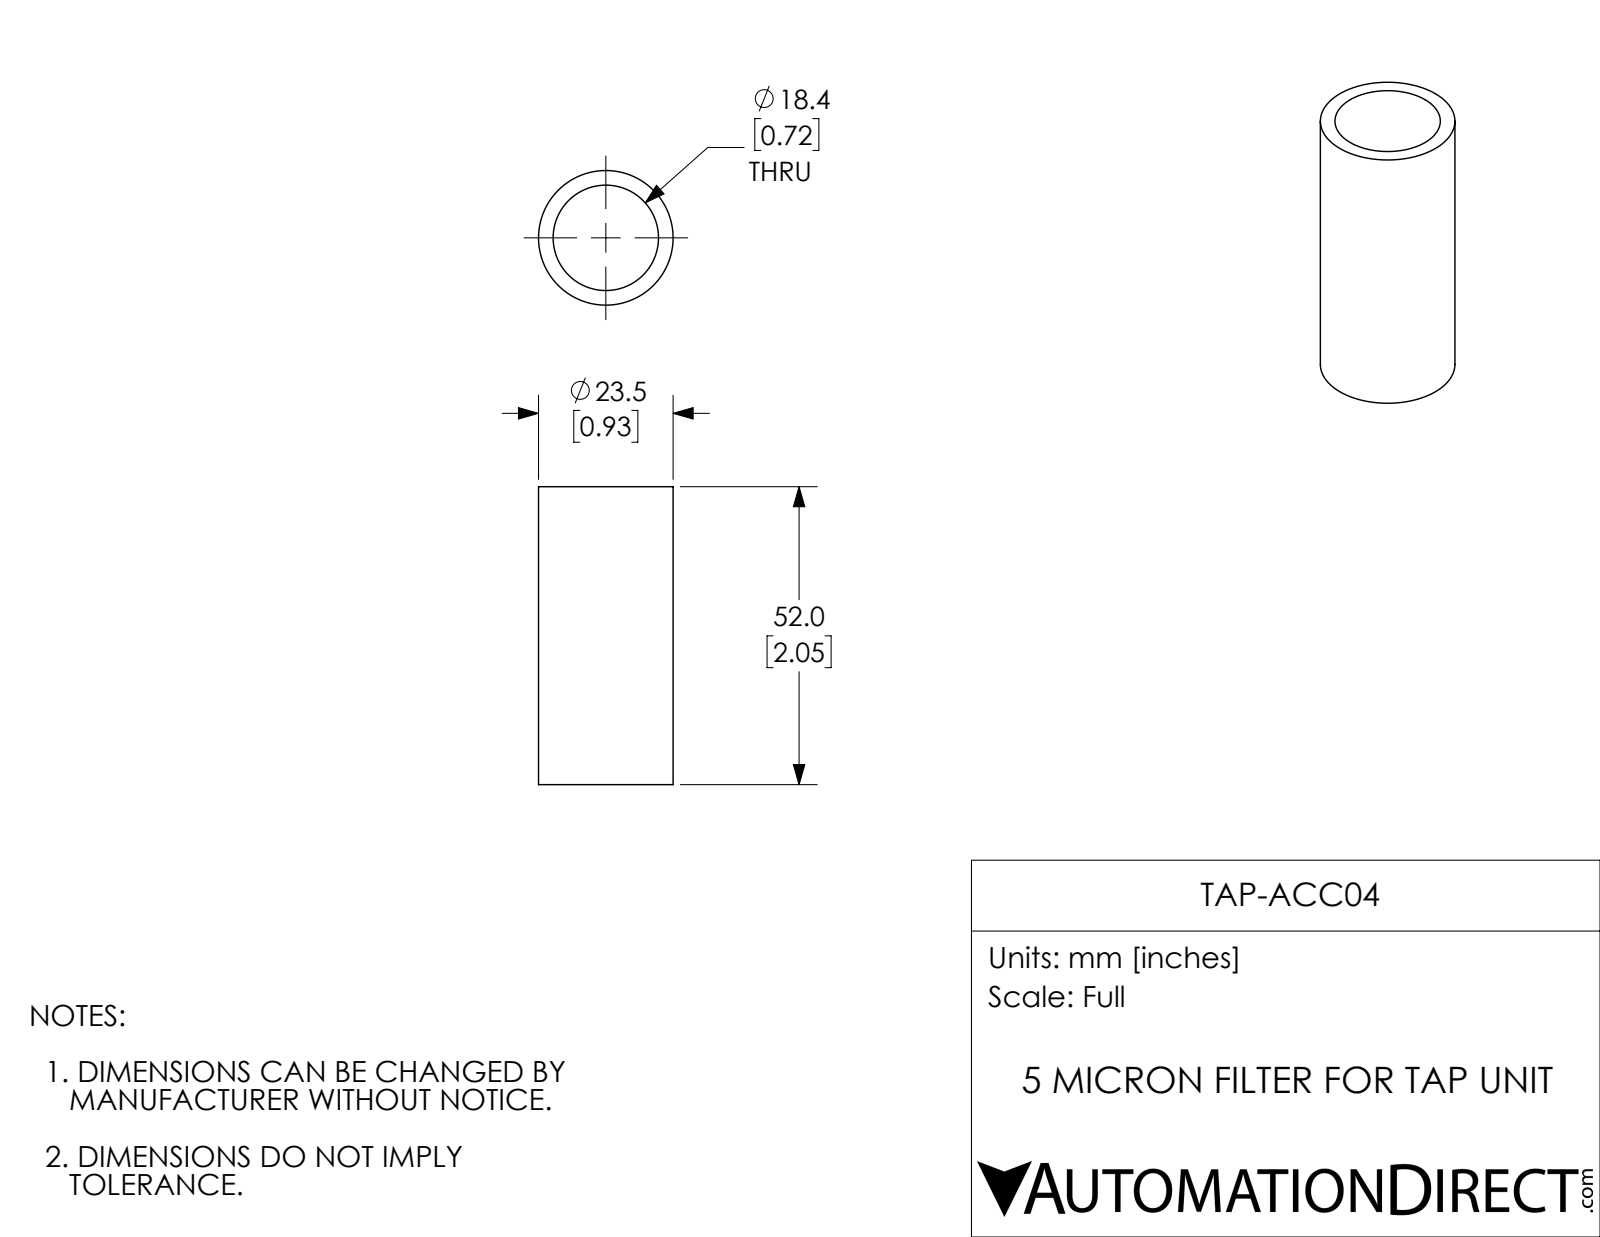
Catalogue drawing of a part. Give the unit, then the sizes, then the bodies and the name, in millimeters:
Units: millimetres
Overall size (bounding box): 52 × 23.5 × 23.5
Round holes (diameter × count): ⌀18.4 ×1
Round bosses / shafts (diameter × count): ⌀23.5 ×1
Main face-to-face distances: 52
Volume: 8 730 mm³ · Surface area: 7 181 mm²
Bodies: 1 solid, 6 faces (2 planar, 4 cylindrical, 0 other)
Part name (STEP PRODUCT): TAP-ACC04
STEP written by: SolidWorks 2017 (AUTOMOTIVE_DESIGN)
